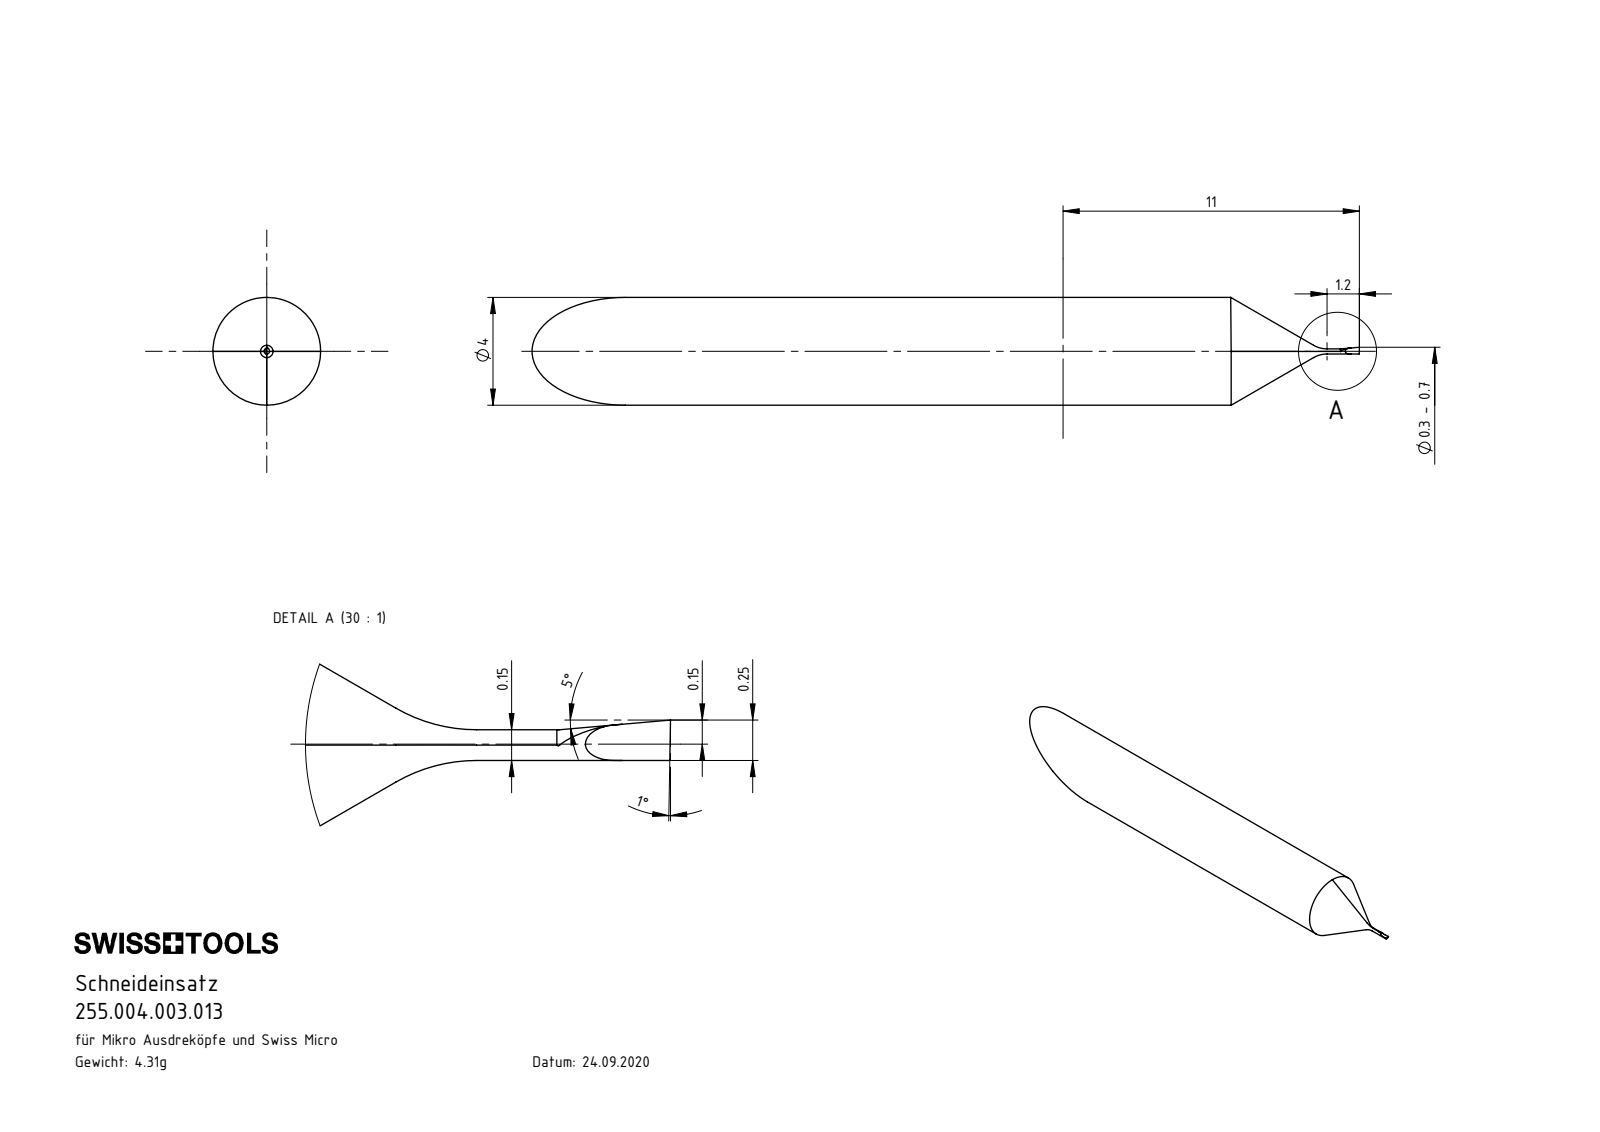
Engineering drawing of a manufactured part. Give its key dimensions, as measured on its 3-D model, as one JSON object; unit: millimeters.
{"part_name": "A04.0010.01.03.00_YR", "step_written_by": "SolidWorks 2017 (AUTOMOTIVE_DESIGN)", "units": "millimeters", "bodies": {"solids": 1, "faces": 26, "planar": 4, "cylindrical": 9, "other": 13}, "overall_size": [30.71, 4, 4], "volume_mm3": 297, "surface_area_mm2": 334, "round_bosses_or_shafts": [[4, 1]], "partial_cylinders_radius": [[0.1, 2], [0.12, 1], [0.16, 1], [0.2, 1]], "face_to_face_distances": [13.45]}
